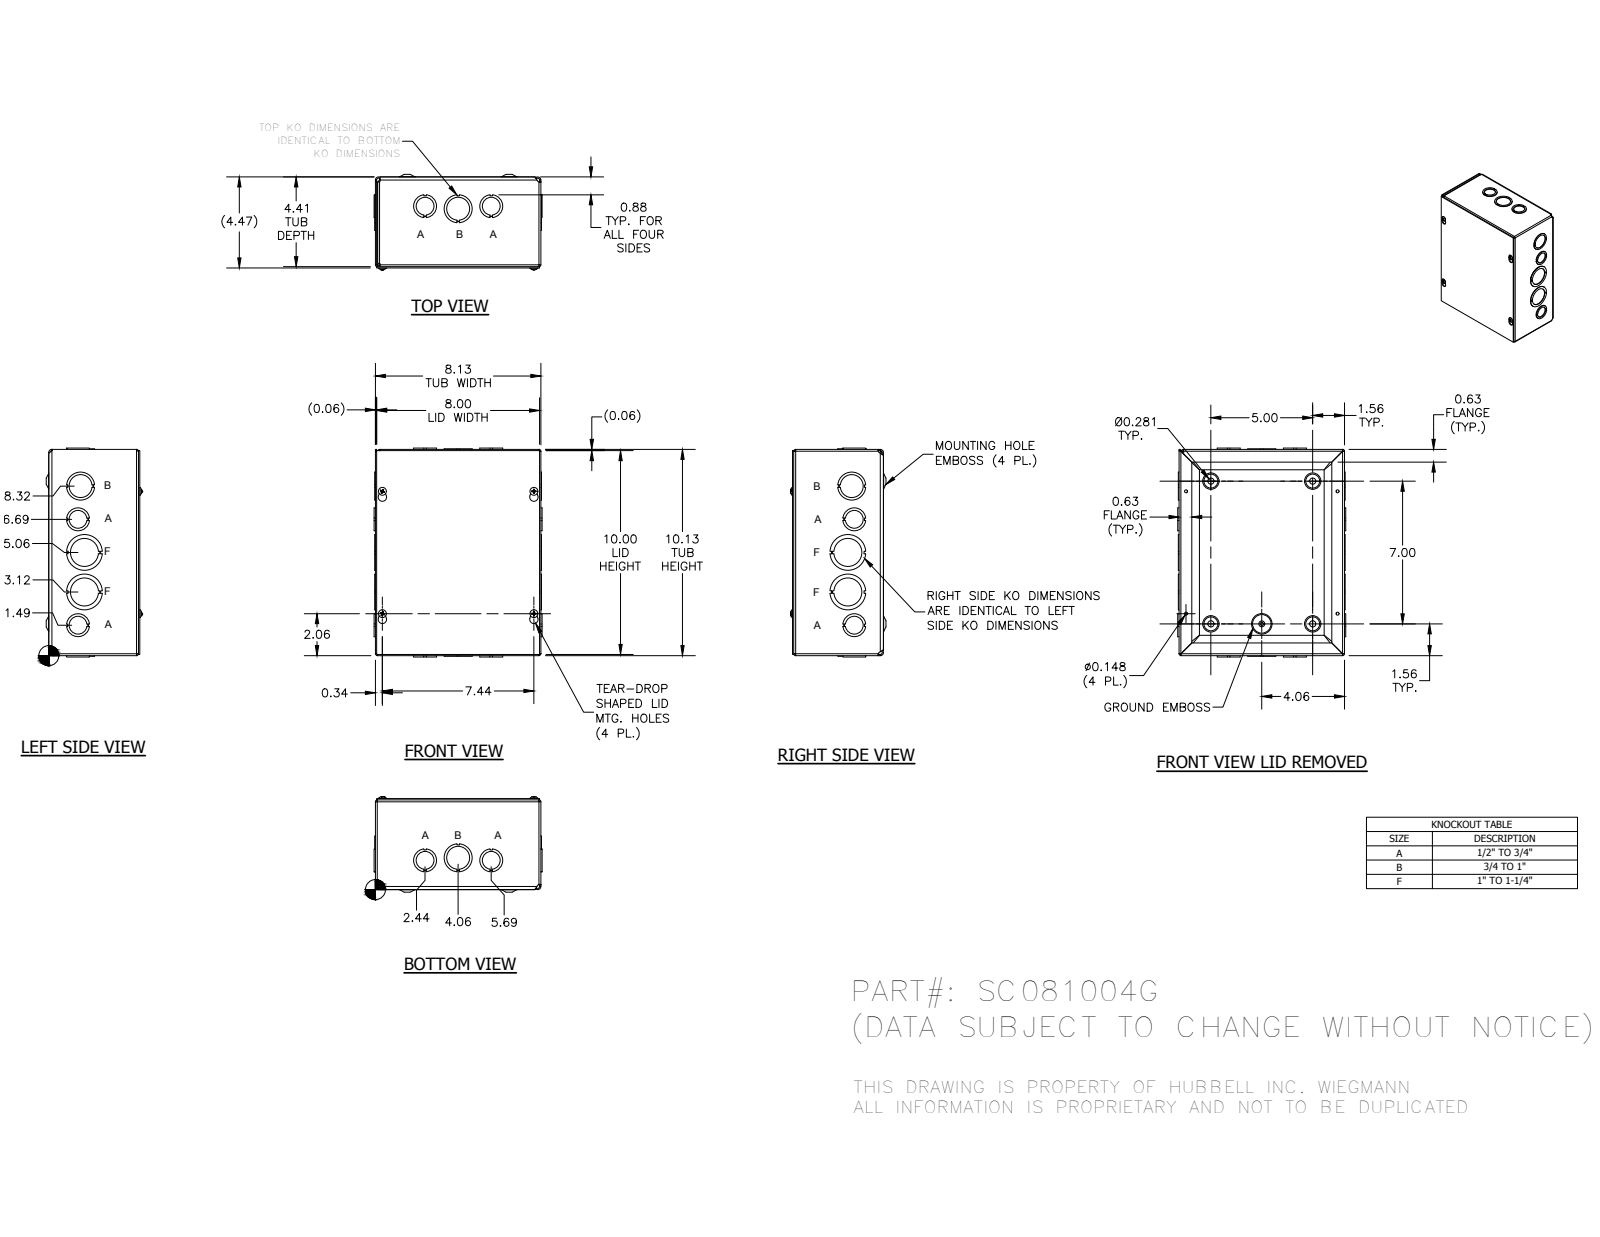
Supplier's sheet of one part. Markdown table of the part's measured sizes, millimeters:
| quantity | value |
| --- | --- |
| part name | SC0810GBKP; SC081004GWRA; SC0810GLID; 34056 (+1 more) |
| STEP written by | Autodesk Inventor 2014 (AUTOMOTIVE_DESIGN) |
| units | millimeters |
| bodies | 22 solids, 806 faces (486 planar, 169 cylindrical, 151 other) |
| overall size | 260.32 × 209.53 × 119.2 |
| round holes (diameter × count) | 28.57 × 6, 3.76 × 4, 7.62 × 4, 22.22 × 4, 34.92 × 4, 44.45 × 2, 4.19 × 1 |
| round bosses / shafts (diameter × count) | 9.75 × 4, 4.17 × 4, 5.8 × 1 |
| partial cylindrical surfaces (radius × count) | 0.79 × 8, 2.37 × 8, 1.4 × 4, 1.57 × 4, 2.38 × 4, 2.79 × 4, 2.97 × 4, 3.15 × 4 |
| main face-to-face distances | 1.57, 110.32, 111.89, 1.59, 111.91, 113.48, 255.6, 1.58, 206.38, 204.8 |
| hole center spacings | 167.98, 228.49, 33.45, 33.46, 42.15, 63.5, 91.03, 127 |
